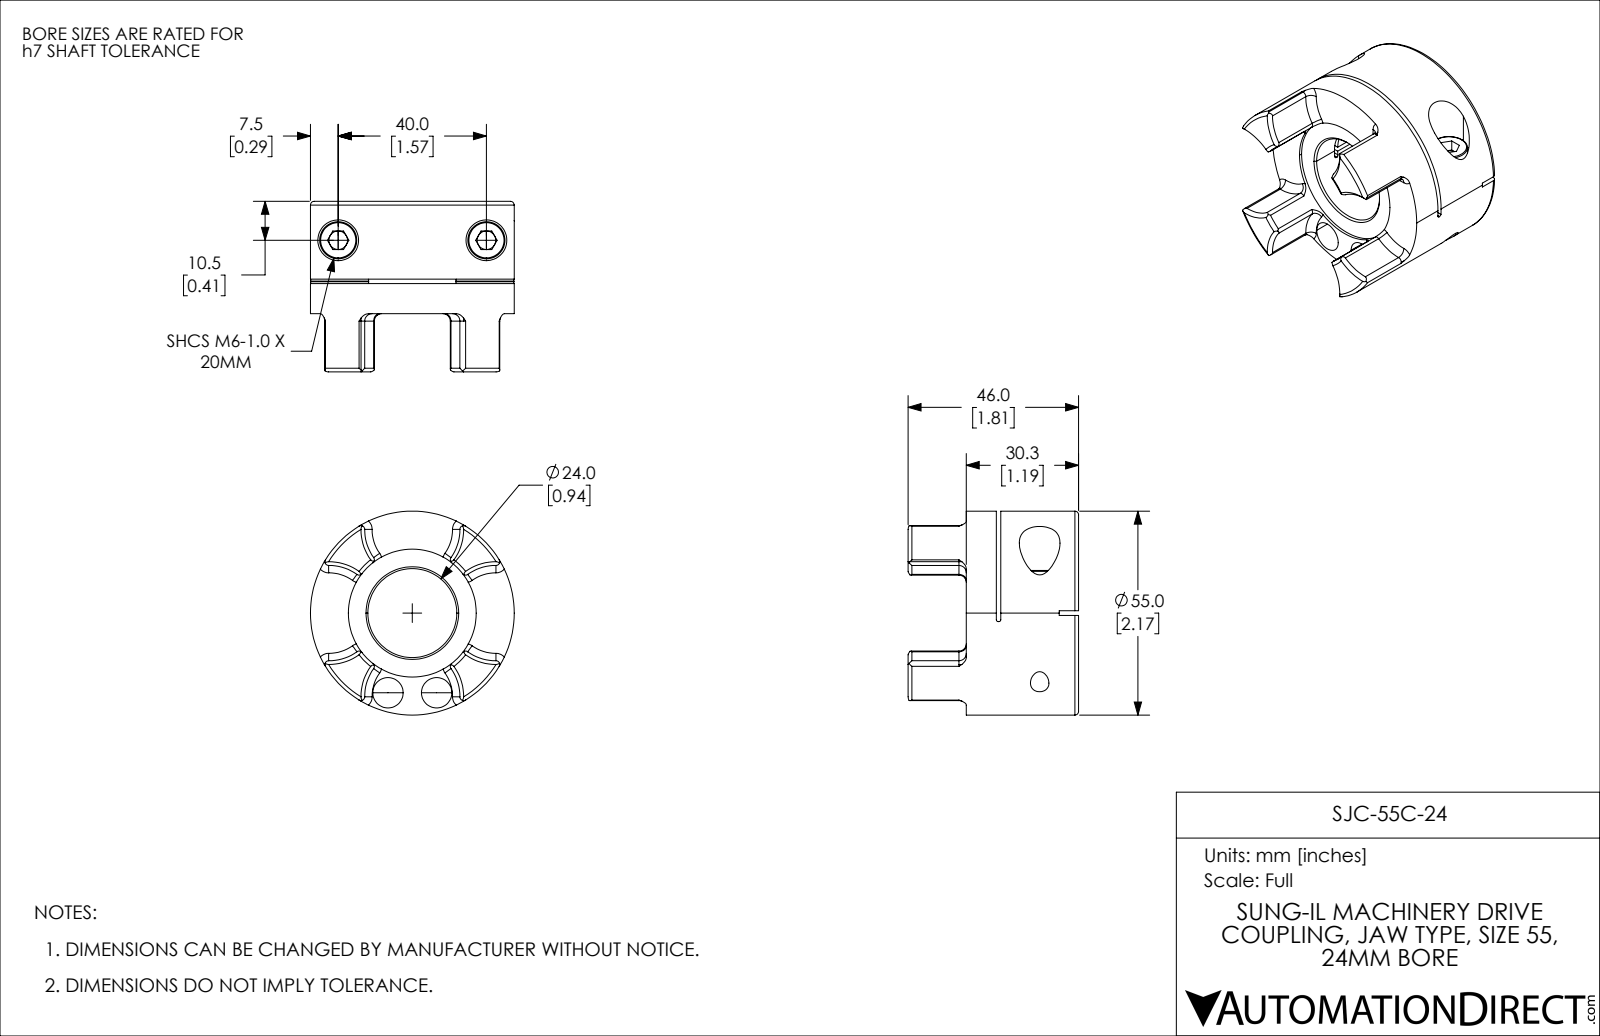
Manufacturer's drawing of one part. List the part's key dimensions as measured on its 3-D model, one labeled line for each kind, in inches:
Part name (STEP PRODUCT): SJC-55C-24
STEP written by: SolidWorks 2021 (CONFIG_CONTROL_DESIGN)
Units: inches
Bodies: 3 solids, 206 faces (52 planar, 72 cylindrical, 82 other)
Overall size (bounding box): 2.165 × 2.165 × 1.811
Volume: 3.622 in³ · Surface area: 30.95 in²
Round holes (diameter × count): ⌀0.197 ×2, ⌀0.252 ×2, ⌀0.323 ×2, ⌀0.433 ×2, ⌀0.945 ×1, ⌀1.358 ×1
Round bosses / shafts (diameter × count): ⌀0.394 ×2, ⌀0.236 ×2, ⌀2.165 ×1
Partial cylindrical surfaces — rounded edges, fillets, slot ends (radius × count): R0.039 ×16, R0.506 ×4, R0.02 ×2, R1.969 ×1
Main face-to-face distances: 0.874, 0.047, 0.827, 0.319, 0.366, 1.193, 0.051, 0.031, 0.287, 0.335
Hole centre spacings: 0.885, 0.517, 1.575
